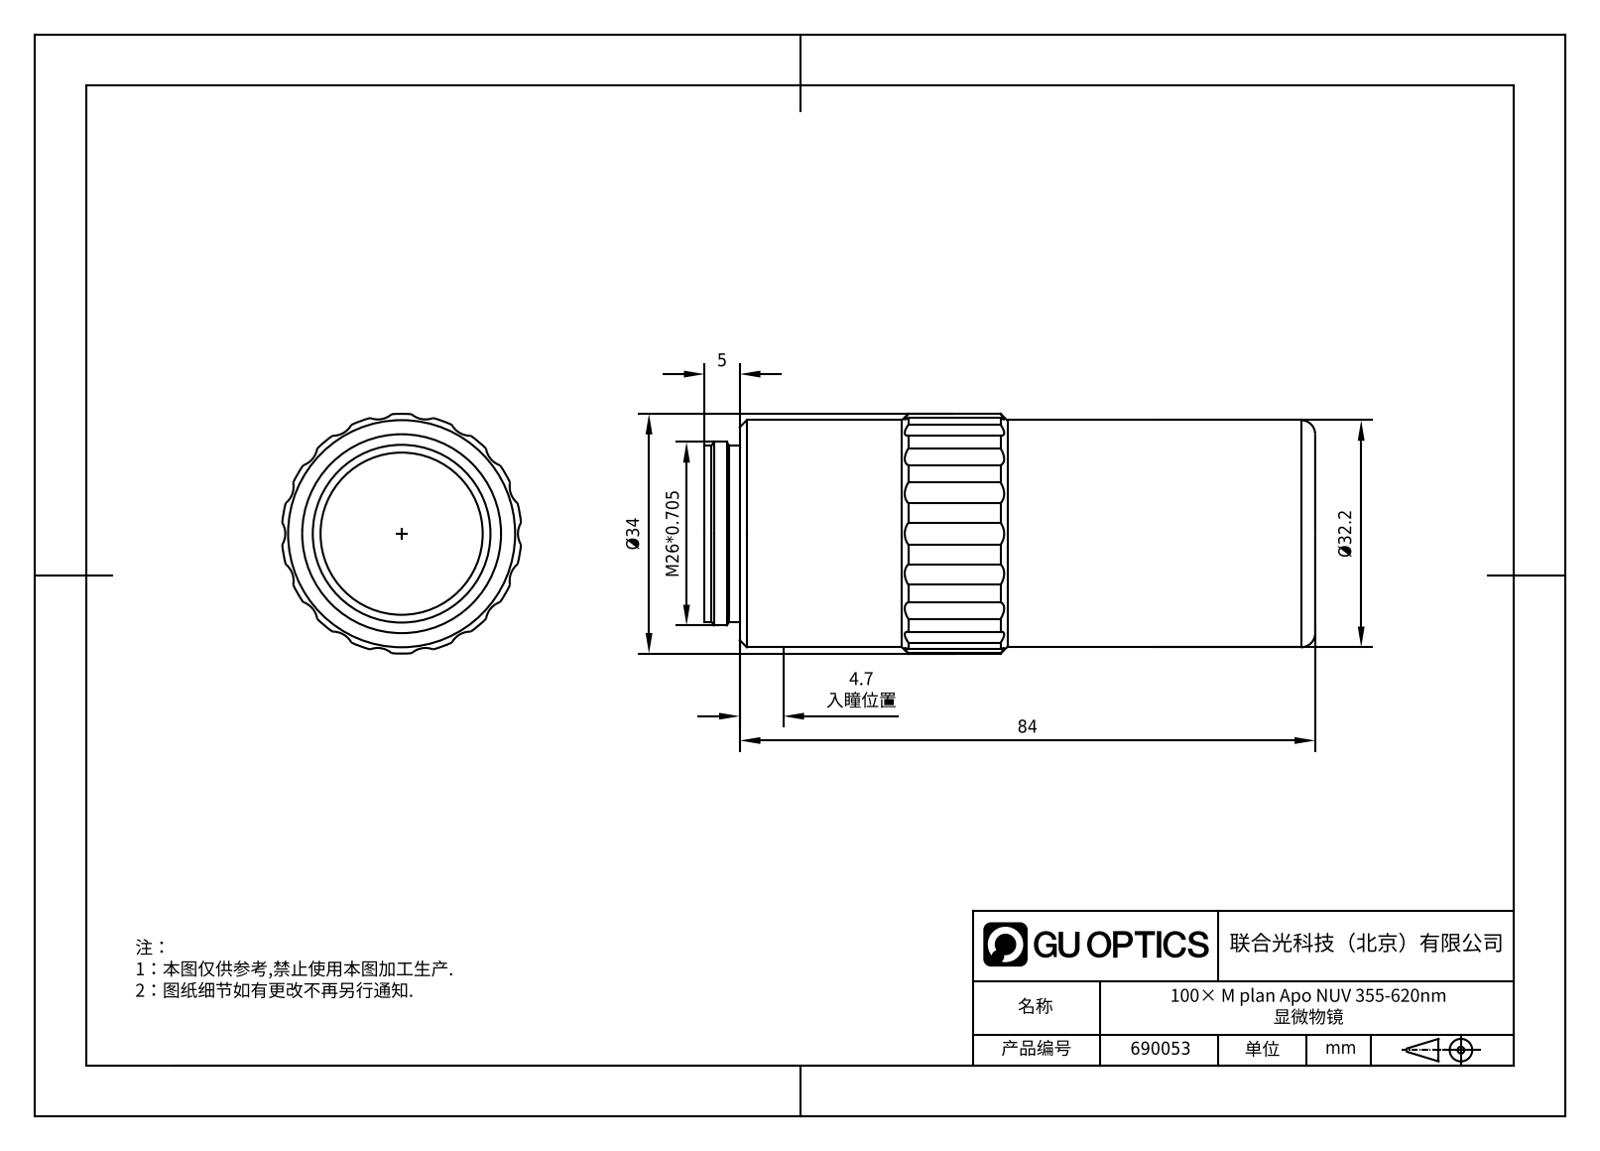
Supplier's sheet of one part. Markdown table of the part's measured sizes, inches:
| quantity | value |
| --- | --- |
| part name | 690053 |
| STEP written by | SolidWorks 2020 (CONFIG_CONTROL_DESIGN) |
| units | inches |
| bodies | 1 solid, 55 faces (6 planar, 43 cylindrical, 6 other) |
| overall size | 3.504 × 1.339 × 1.333 |
| volume | 4.372 in³ |
| surface area | 16.54 in² |
| round holes (diameter × count) | 0.157 × 1, 0.63 × 1 |
| round bosses / shafts (diameter × count) | 1.268 × 1, 1.024 × 1, 0.984 × 1 |
| partial cylindrical surfaces (radius × count) | 0.118 × 18, 0.669 × 1 |
| main face-to-face distances | 3.504, 0.197, 3.307, 0.039, 3.465, 3.268, 0.157, 3.425, 1.693, 1.654 |
